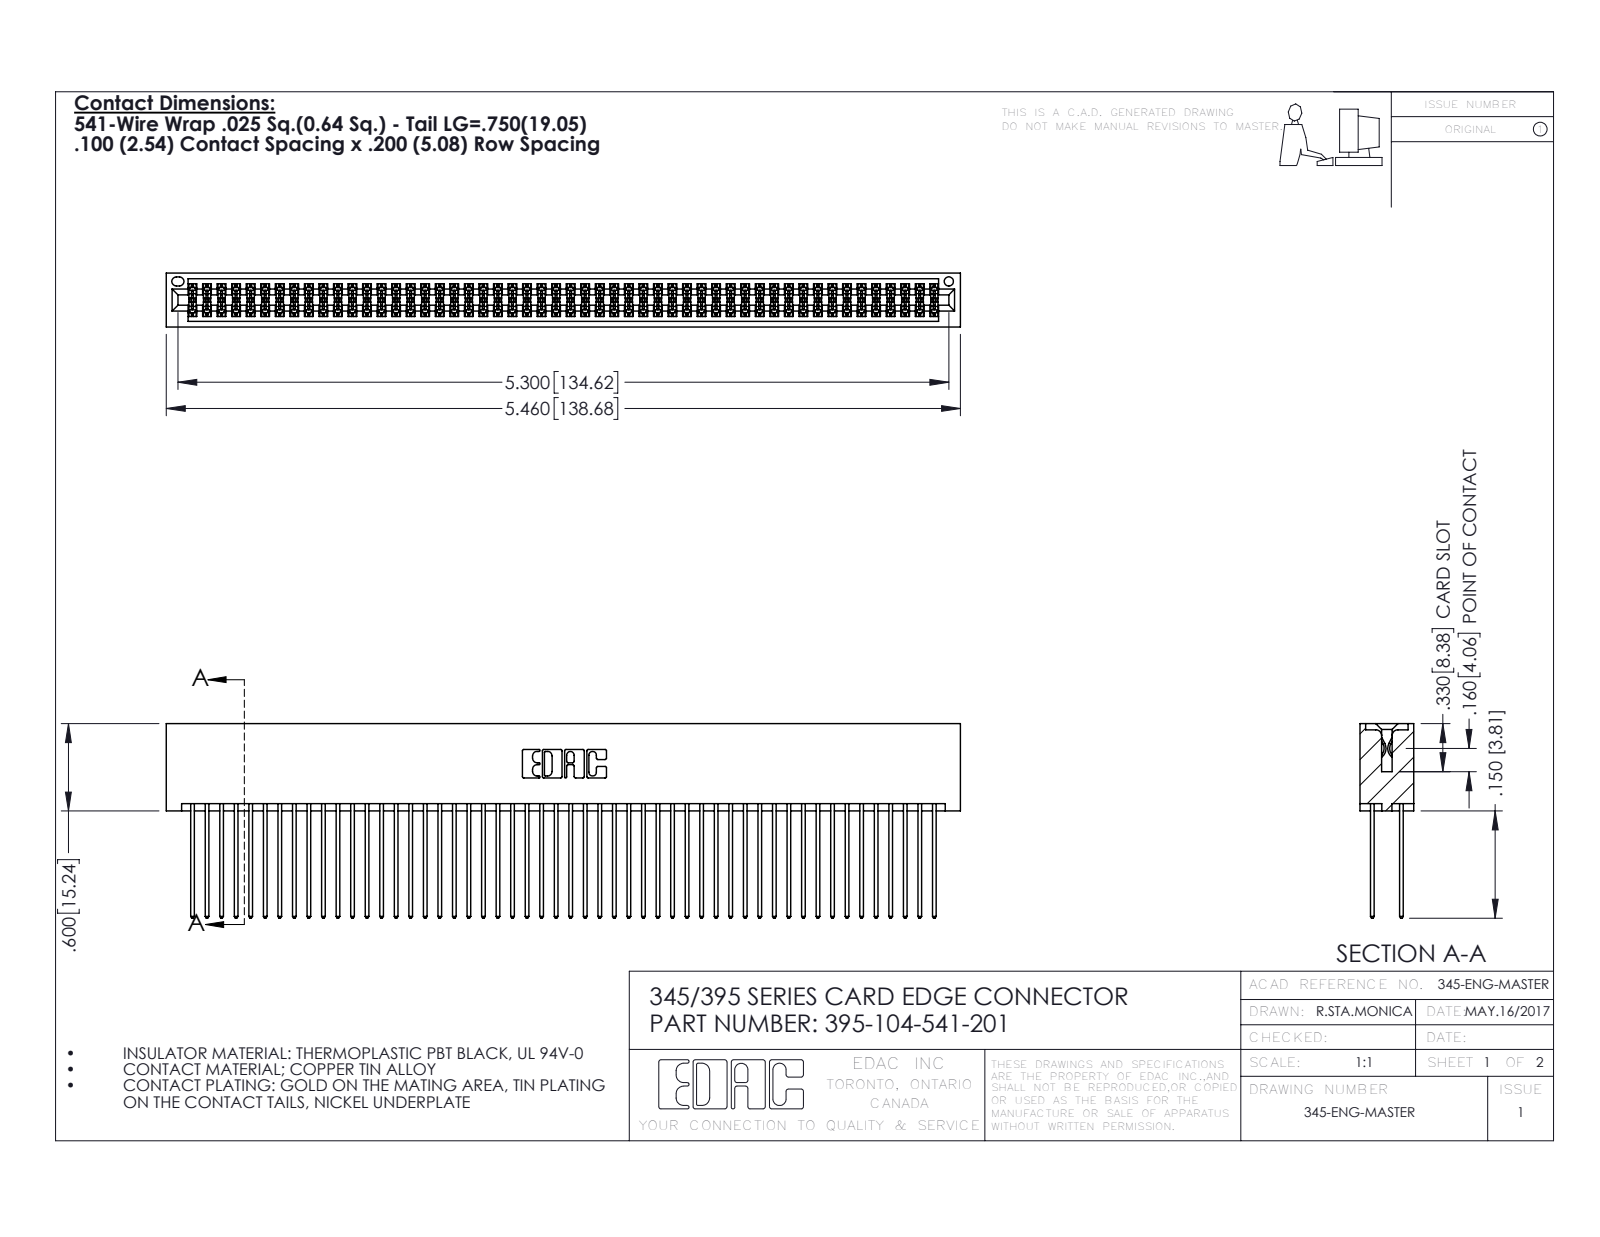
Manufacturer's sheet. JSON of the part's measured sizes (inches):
{"part_name": "395-104-541-201; 345 Part_No Mounting Lugs; 345-292-001_345-293-141", "step_written_by": "SolidWorks 2016 (CONFIG_CONTROL_DESIGN)", "units": "inches", "bodies": {"solids": 105, "faces": 5318, "planar": 3508, "cylindrical": 1810, "other": 0}, "overall_size": [5.46, 1.337, 0.37], "volume_in3": 0.902, "surface_area_in2": 38.97, "round_holes": [[0.064, 1]], "partial_cylinders_radius": [[0.006, 156], [0.01, 104], [0.01, 22], [0.007, 6], [0.031, 6], [0.026, 3], [0.014, 2], [0.019, 2]], "face_to_face_distances": [0.298, 0.072, 0.2, 0.098, 0.272, 0.025, 0.225, 0.37, 0.175, 0.149]}
